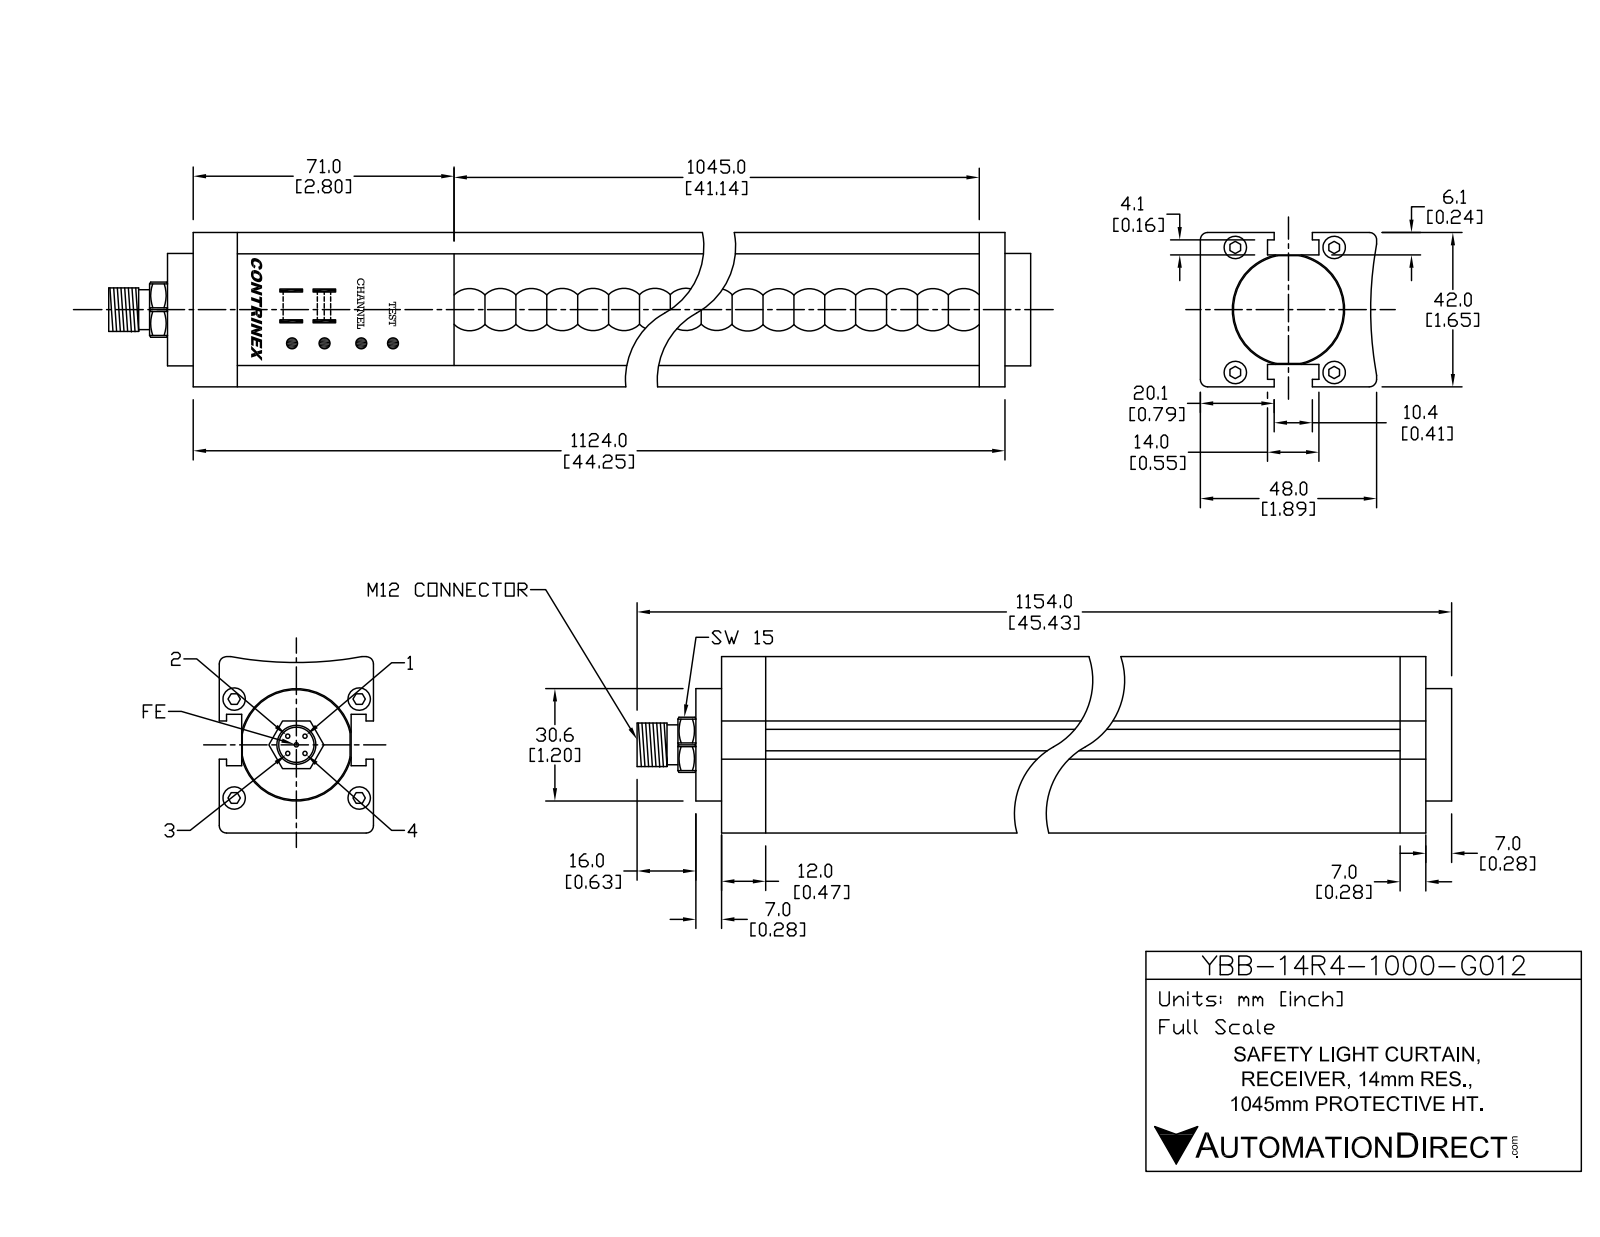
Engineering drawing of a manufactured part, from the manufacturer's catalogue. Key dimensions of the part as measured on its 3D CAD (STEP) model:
Part name (STEP PRODUCT): YBB-14R4-1000-G012
STEP written by: SolidWorks 2016 (AUTOMOTIVE_DESIGN)
Units: millimetres
Bodies: 19 solids, 440 faces (208 planar, 168 cylindrical, 64 other)
Overall size (bounding box): 1154 × 48 × 42
Volume: 2 022 000 mm³ · Surface area: 257 353 mm²
Round holes (diameter × count): ⌀6 ×4, ⌀8.5 ×1, ⌀32 ×1
Round bosses / shafts (diameter × count): ⌀1 ×5, ⌀5.5 ×4, ⌀30.6 ×1, ⌀12 ×1, ⌀10.5 ×1
Partial cylindrical surfaces — rounded edges, fillets, slot ends (radius × count): R1 ×48, R0.5 ×4, R0.55 ×2, R8.2 ×1, R100 ×1
Main face-to-face distances: 6.3, 35.7, 42, 29.4, 14, 17.2, 31.2, 15.7, 29.7, 46.9
Hole centre spacings: 21.04, 22.34, 26.9, 34, 43.35
